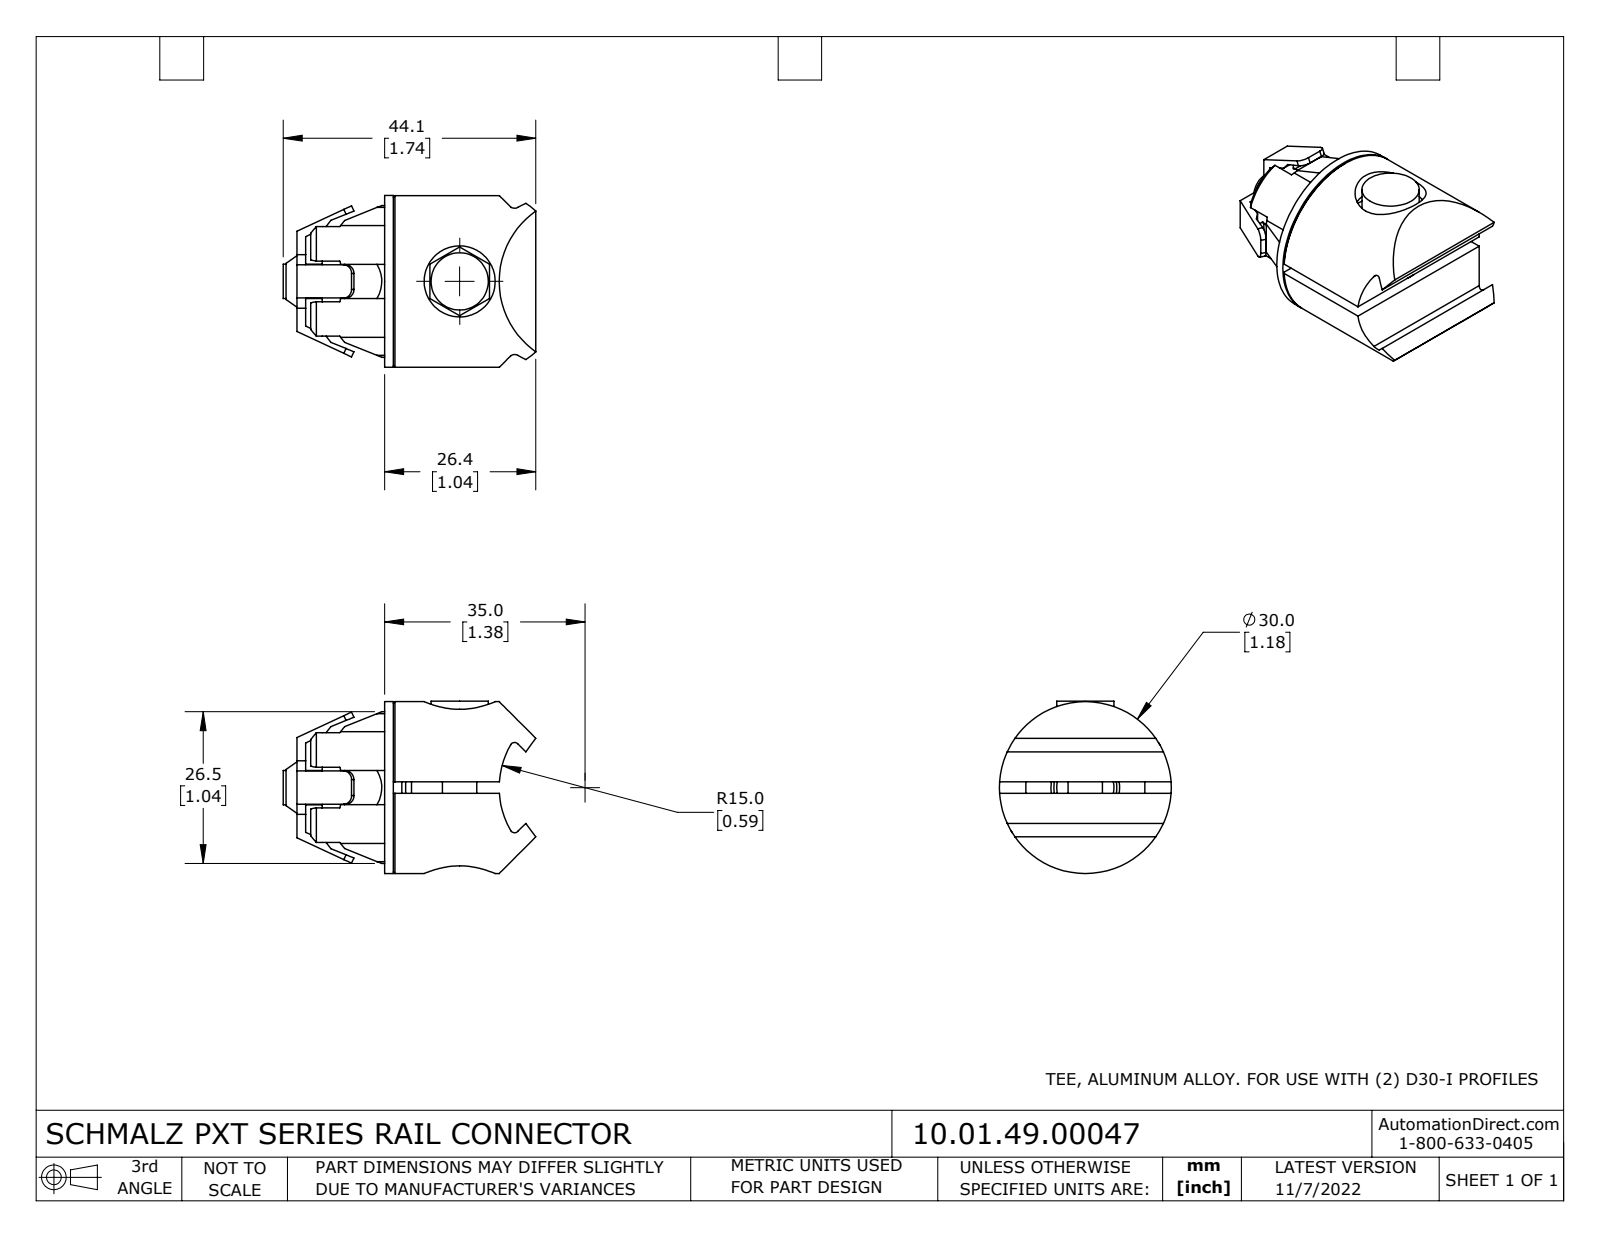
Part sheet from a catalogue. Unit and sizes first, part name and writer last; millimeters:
Units: millimetres
Overall size (bounding box): 44.1 × 30.1 × 30
Round holes (diameter × count): ⌀5 ×2, ⌀6.6 ×2, ⌀10 ×1, ⌀12.4 ×1, ⌀18.5 ×1, ⌀22 ×1
Round bosses / shafts (diameter × count): ⌀6 ×2, ⌀30 ×1, ⌀20.8 ×1, ⌀11 ×1, ⌀10 ×1, ⌀9.9 ×1
Partial cylindrical surfaces — rounded edges, fillets, slot ends (radius × count): R1.5 ×8, R6.75 ×4, R0.8 ×2, R10.2 ×1, R13.25 ×1, R15 ×1
Main face-to-face distances: 1.5, 3.2, 2, 4, 5.5, 15.3, 6.5, 8.5, 4.7, 0.8
Volume: 18 010 mm³ · Surface area: 11 524 mm²
Bodies: 8 solids, 200 faces (109 planar, 73 cylindrical, 18 other)
Part name (STEP PRODUCT): 10.01.49.00047
STEP written by: SolidWorks 2021 (CONFIG_CONTROL_DESIGN)
